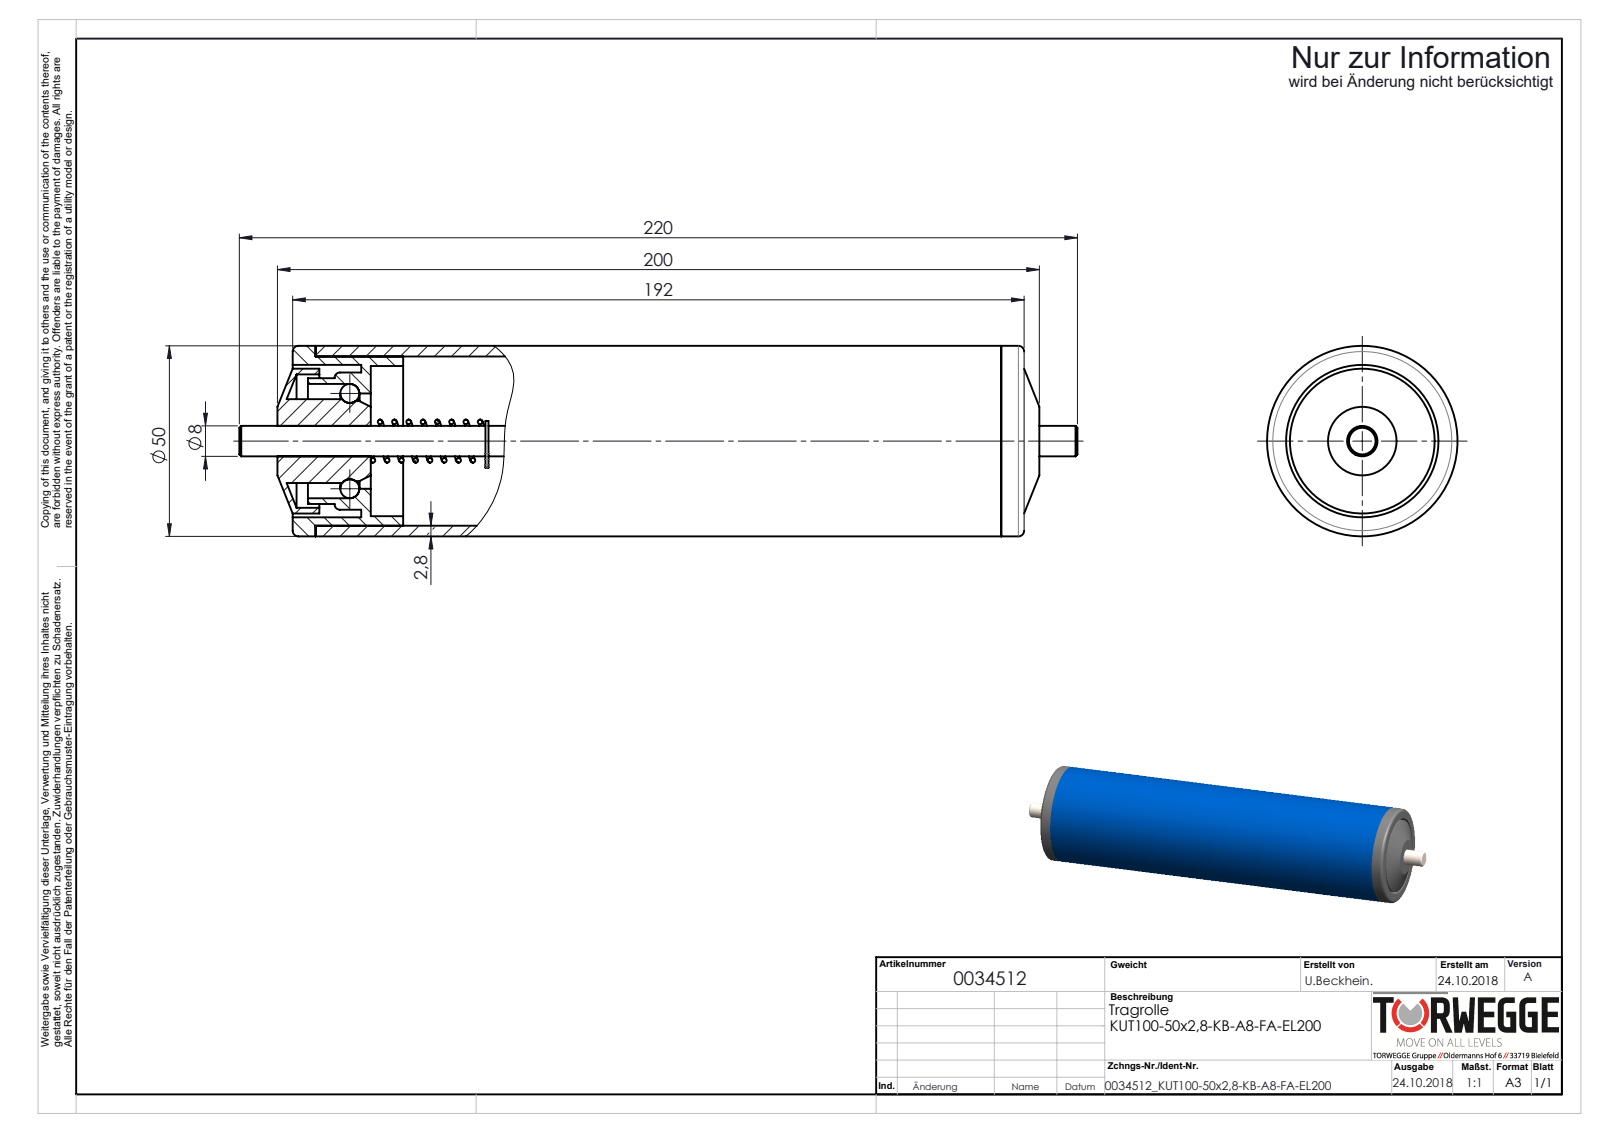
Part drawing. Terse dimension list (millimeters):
name: 0034512_KUT100-50x2,8-KB-A8-FA-EL200
written by: SolidWorks 2018 (AUTOMOTIVE_DESIGN)
unit: mm
bodies: 11 solids, 186 faces (52 planar, 88 cylindrical, 46 other)
size: 220 × 50 × 50
volume: 141 775 mm³; area: 101 432 mm²
holes: 1× ⌀7.6, 1× ⌀8, 1× ⌀25, 1× ⌀30, 1× ⌀35, 1× ⌀39.4, 1× ⌀40
bosses: 1× ⌀50, 1× ⌀44.4, 1× ⌀38, 1× ⌀36, 1× ⌀33, 1× ⌀22, 1× ⌀21
rounds: 2× R0.6, 2× R0.75, 2× R2.45, 1× R4.87, 1× R7
face distances: 14.5, 165.5, 11, 6, 20.5, 171.5, 186, 151, 180, 192
